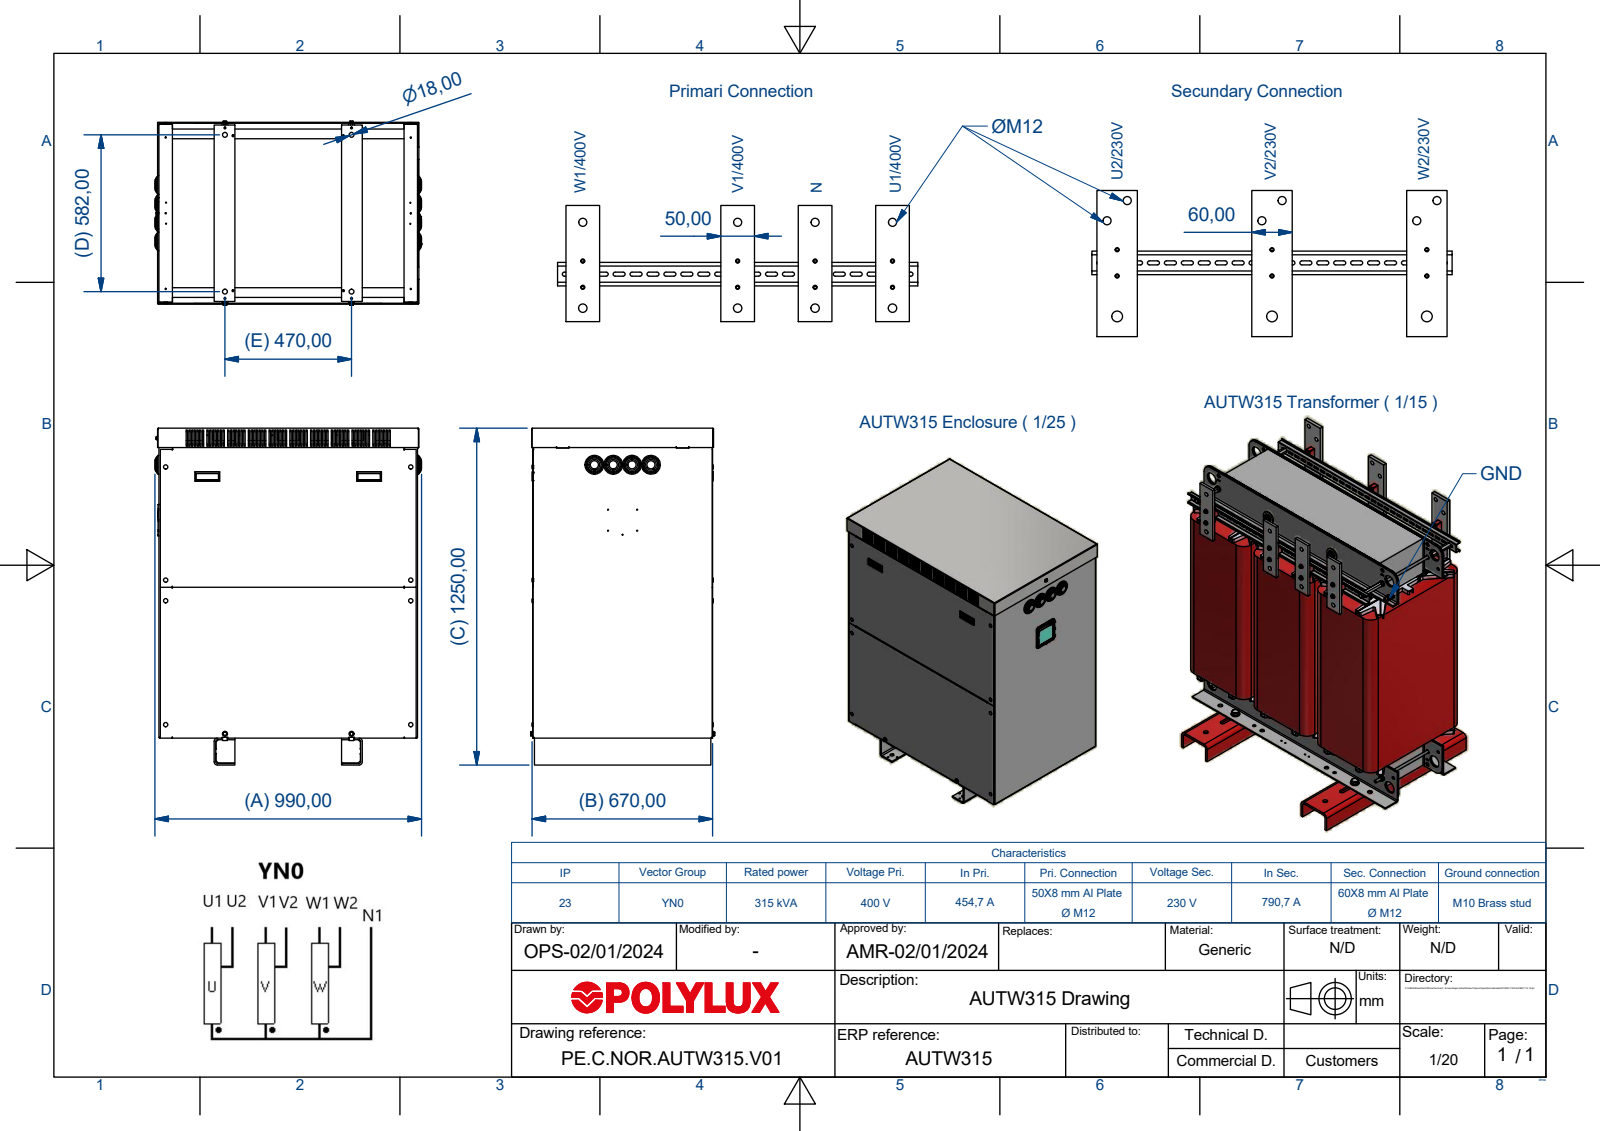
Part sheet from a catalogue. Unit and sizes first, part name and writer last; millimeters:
Units: millimetres
Overall size (bounding box): 1250 × 990 × 675
Round holes (diameter × count): ⌀3.5 ×46, ⌀13 ×26, ⌀12 ×24, ⌀5 ×19, ⌀7 ×16, ⌀9 ×16, ⌀4 ×15, ⌀11.5 ×14, ⌀4.5 ×12, ⌀6 ×12, ⌀6.7 ×10, ⌀5.3 ×8
Round bosses / shafts (diameter × count): ⌀15 ×12, ⌀6.7 ×8, ⌀4.6 ×8, ⌀8 ×7, ⌀70 ×4, ⌀65 ×4, ⌀63 ×4, ⌀57 ×4
Partial cylindrical surfaces — rounded edges, fillets, slot ends (radius × count): R1.5 ×114, R3 ×95, R3.5 ×60, R3.8 ×24, R10 ×24, R0.5 ×22, R0.8 ×12, R30 ×12
Main face-to-face distances: 1.5, 666.5, 958.5, 665, 3, 668, 173.5, 250, 3.3, 170.3
Hole centre spacings: 120, 67.1, 70, 182.5, 240, 140, 910, 301.5
Bodies: 242 solids, 10415 faces (6804 planar, 1438 cylindrical, 2173 other)
Part name (STEP PRODUCT): AUTW315; PN. CAJ.RC110_IP23.V0; LateralCAJ.RC110_IP23; Pasacables_v18 (+5 more)
STEP written by: Autodesk Inventor 2018 (AUTOMOTIVE_DESIGN)
